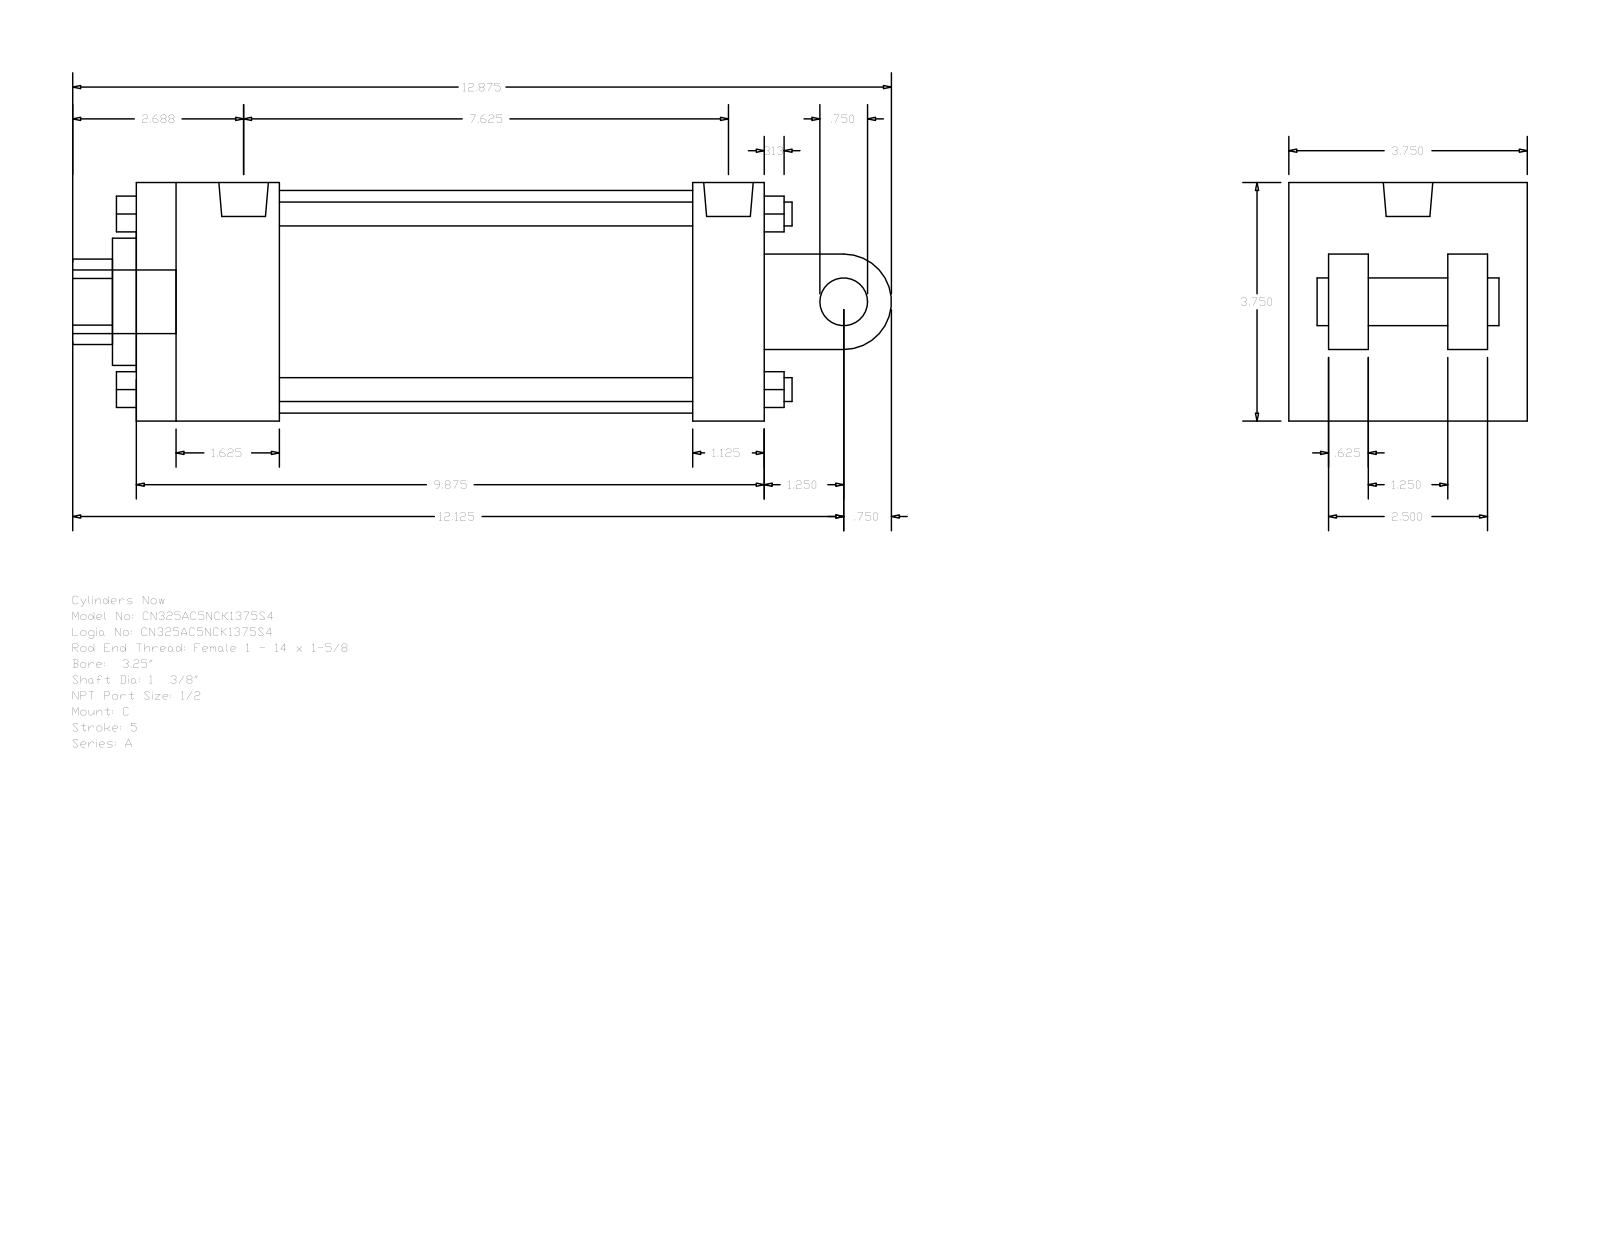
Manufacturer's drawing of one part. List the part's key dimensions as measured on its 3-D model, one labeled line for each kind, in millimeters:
Part name (STEP PRODUCT): A_C__0325_1.375
STEP written by: GSSL Pune (CONFIG_CONTROL_DESIGN)
Units: millimetres
Bodies: 0 solids, 135 faces (102 planar, 33 cylindrical, 0 other)
Overall size (bounding box): 327.02 × 95.25 × 95.25
Round holes (diameter × count): ⌀8.73 ×2, ⌀19.77 ×1, ⌀34.92 ×1, ⌀50.8 ×1, ⌀88.9 ×1
Round bosses / shafts (diameter × count): ⌀9.53 ×4, ⌀8.73 ×2, ⌀25.4 ×1, ⌀19.77 ×1, ⌀19.05 ×1
Partial cylindrical surfaces — rounded edges, fillets, slot ends (radius × count): R17.06 ×1, R19.05 ×1
Main face-to-face distances: 95.24, 15.87, 250.83, 63.5, 66.67, 28.58, 79.37, 31.74, 47.63, 222.25
Hole centre spacings: 3.18
